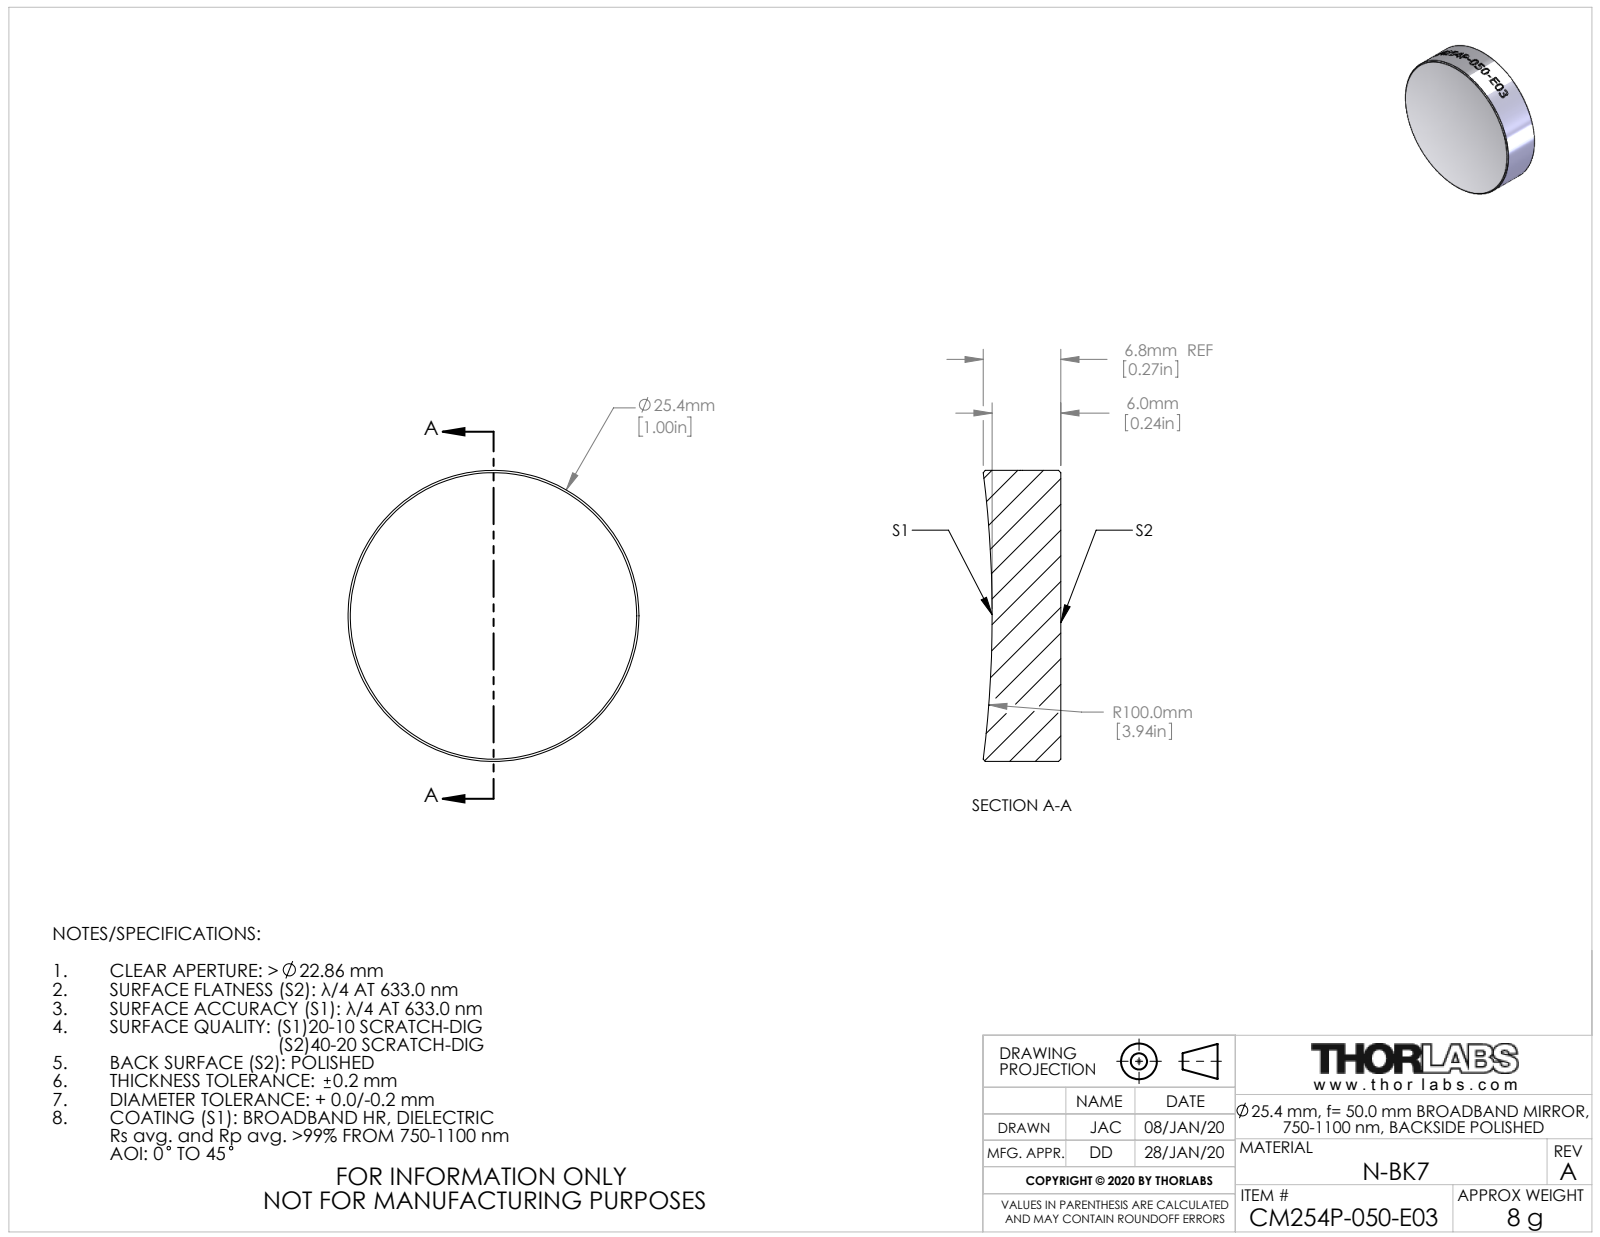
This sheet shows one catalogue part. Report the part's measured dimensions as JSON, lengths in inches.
{"part_name": "TTN201390-E0W", "step_written_by": "SolidWorks 2018 (CONFIG_CONTROL_DESIGN)", "units": "inches", "bodies": {"solids": 1, "faces": 28, "planar": 1, "cylindrical": 21, "other": 6}, "overall_size": [1, 1, 0.267], "volume_in3": 0.198, "surface_area_in2": 2.385, "round_bosses_or_shafts": [[1, 1]]}
